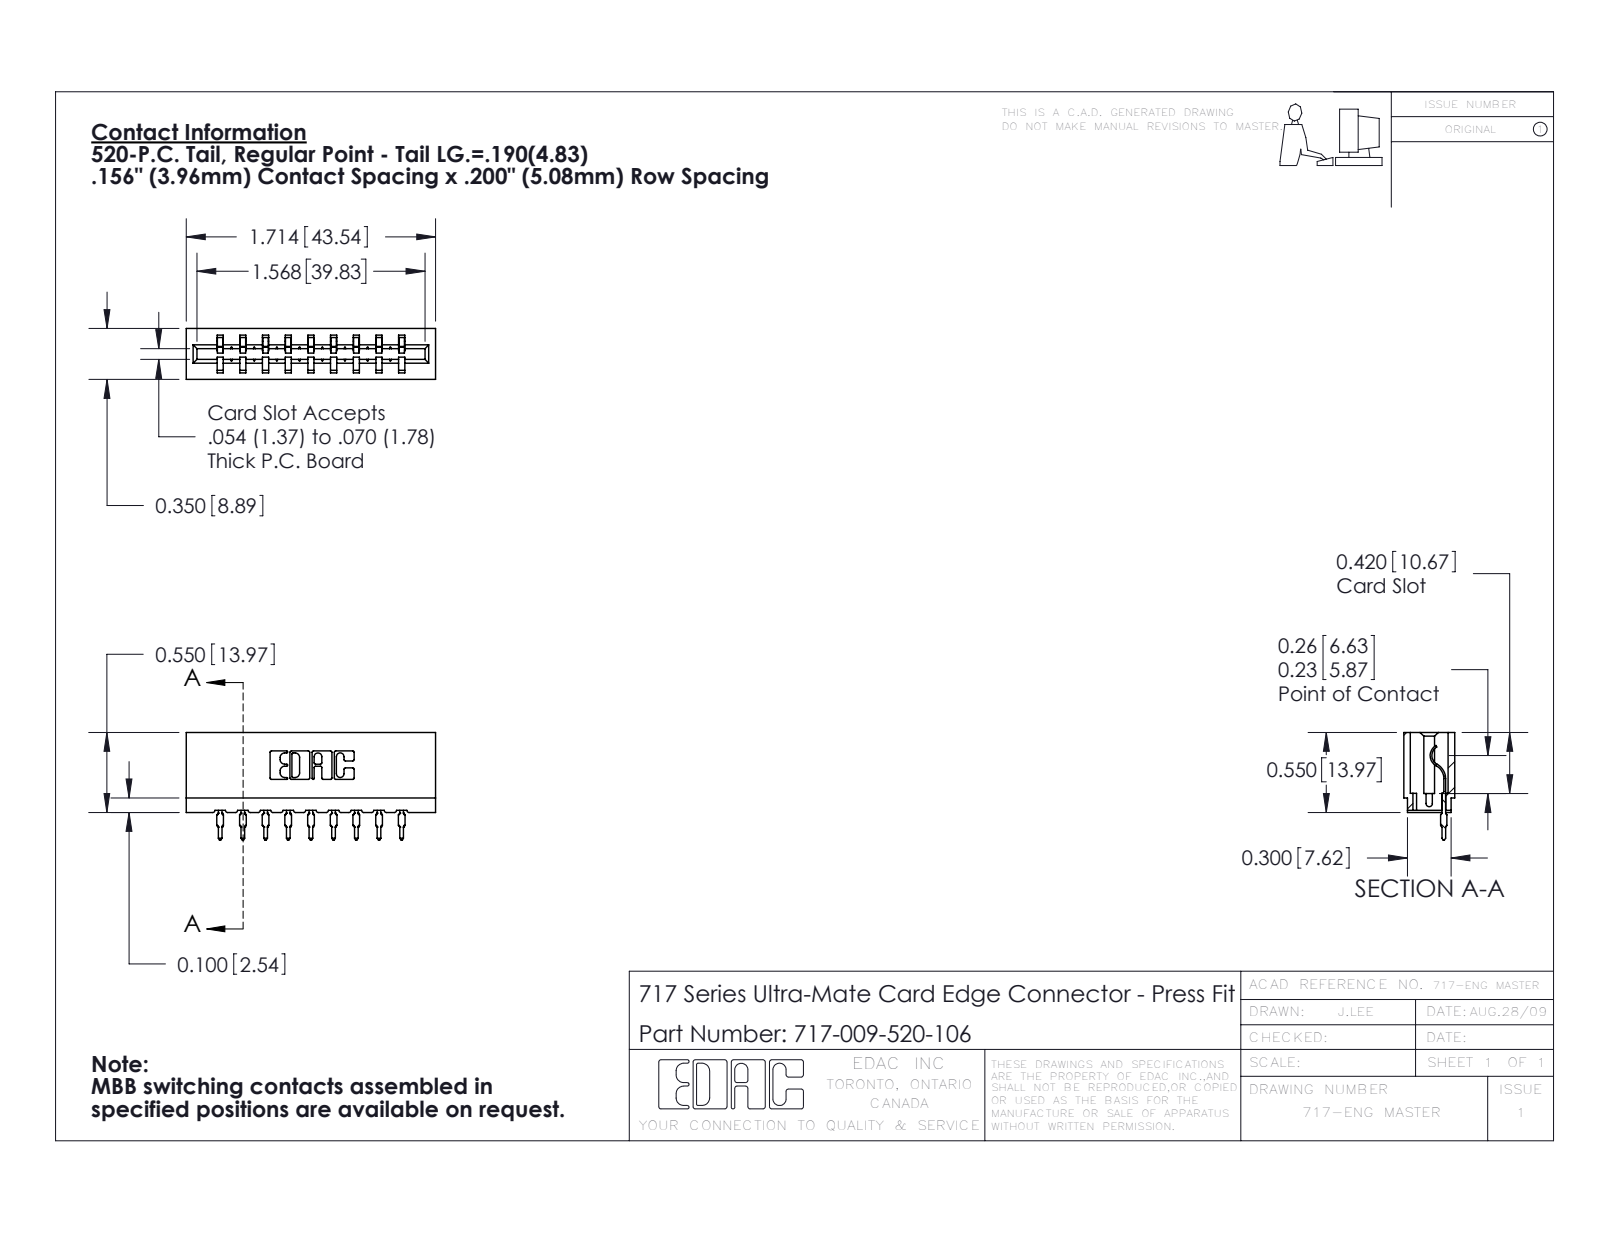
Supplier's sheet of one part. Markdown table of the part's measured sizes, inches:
| quantity | value |
| --- | --- |
| part name | 717 Part_Insulator Option - 06; 745-292-001_520; 717-009-520-106 |
| STEP written by | SolidWorks 2016 (CONFIG_CONTROL_DESIGN) |
| units | inches |
| bodies | 10 solids, 1111 faces (666 planar, 211 cylindrical, 234 other) |
| overall size | 1.714 × 0.739 × 0.35 |
| volume | 0.233 in³ |
| surface area | 7.648 in² |
| partial cylindrical surfaces (radius × count) | 0.01 × 22, 0.015 × 18, 0.021 × 18, 0.007 × 6, 0.031 × 6, 0.005 × 4, 0.011 × 4, 0.026 × 3 |
| main face-to-face distances | 0.156, 0.212, 0.624, 0.138, 0.468, 0.198, 0.35, 0.312, 0.042, 0.312 |
